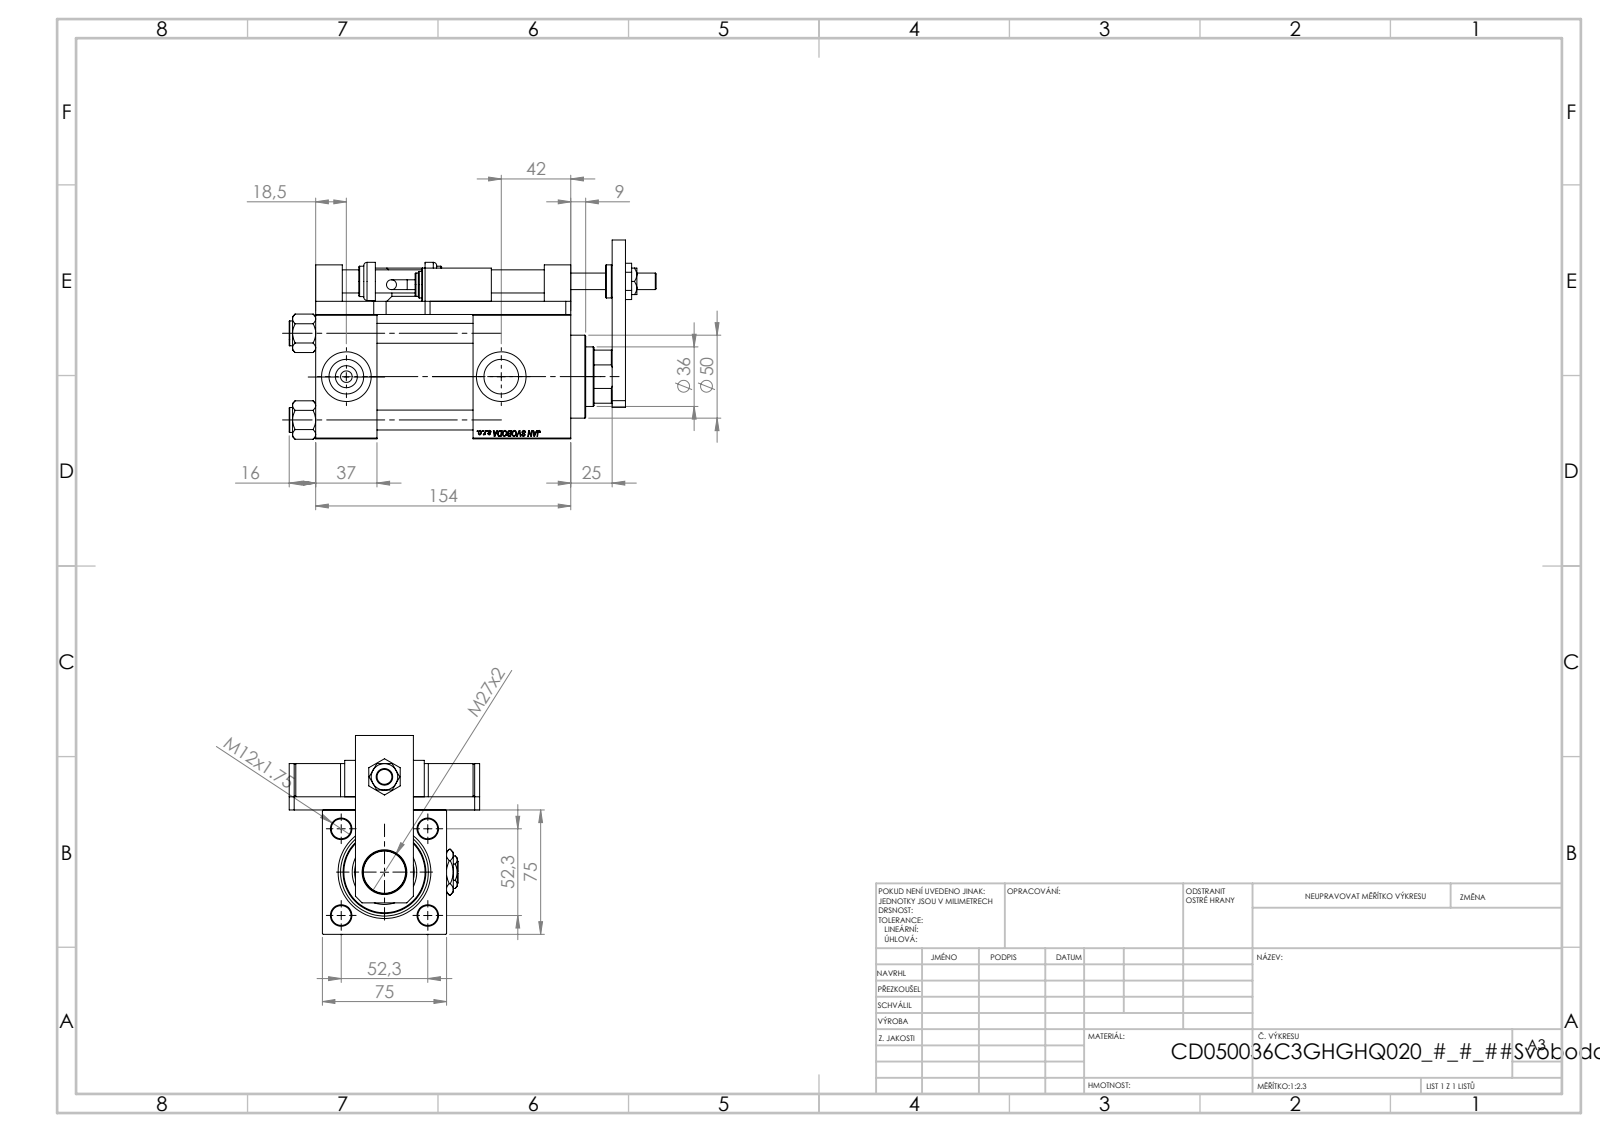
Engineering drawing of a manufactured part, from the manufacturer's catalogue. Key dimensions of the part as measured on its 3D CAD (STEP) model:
Part name (STEP PRODUCT): NUT_M5_V215CD_C; V215CD_SWITCH_Q_NUT10; V215CD_SWITCH_Q_NUT; V215CD_SWITCH_Q_TYC (+8 more)
STEP written by: SolidWorks 2019 (CONFIG_CONTROL_DESIGN)
Units: millimetres
Bodies: 26 solids, 1477 faces (694 planar, 166 cylindrical, 617 other)
Overall size (bounding box): 221.5 × 120.27 × 115
Volume: 935 996 mm³ · Surface area: 242 484 mm²
Round holes (diameter × count): ⌀8.5 ×4, ⌀12 ×4, ⌀13.5 ×4, ⌀7 ×2, ⌀20.96 ×2, ⌀30 ×2, ⌀10 ×1, ⌀14 ×1, ⌀25.5 ×1, ⌀27 ×1, ⌀36 ×1, ⌀39 ×1
Round bosses / shafts (diameter × count): ⌀15 ×4, ⌀20 ×3, ⌀16 ×2, ⌀14 ×2, ⌀6 ×2, ⌀56 ×1, ⌀50 ×1, ⌀23 ×1
Partial cylindrical surfaces — rounded edges, fillets, slot ends (radius × count): R7.5 ×4, R17.5 ×1
Main face-to-face distances: 8, 75, 20, 37, 83, 95, 154, 92, 59, 117
Hole centre spacings: 36.98, 52.3, 32, 40.82, 73.96, 87.64, 138, 141.66
